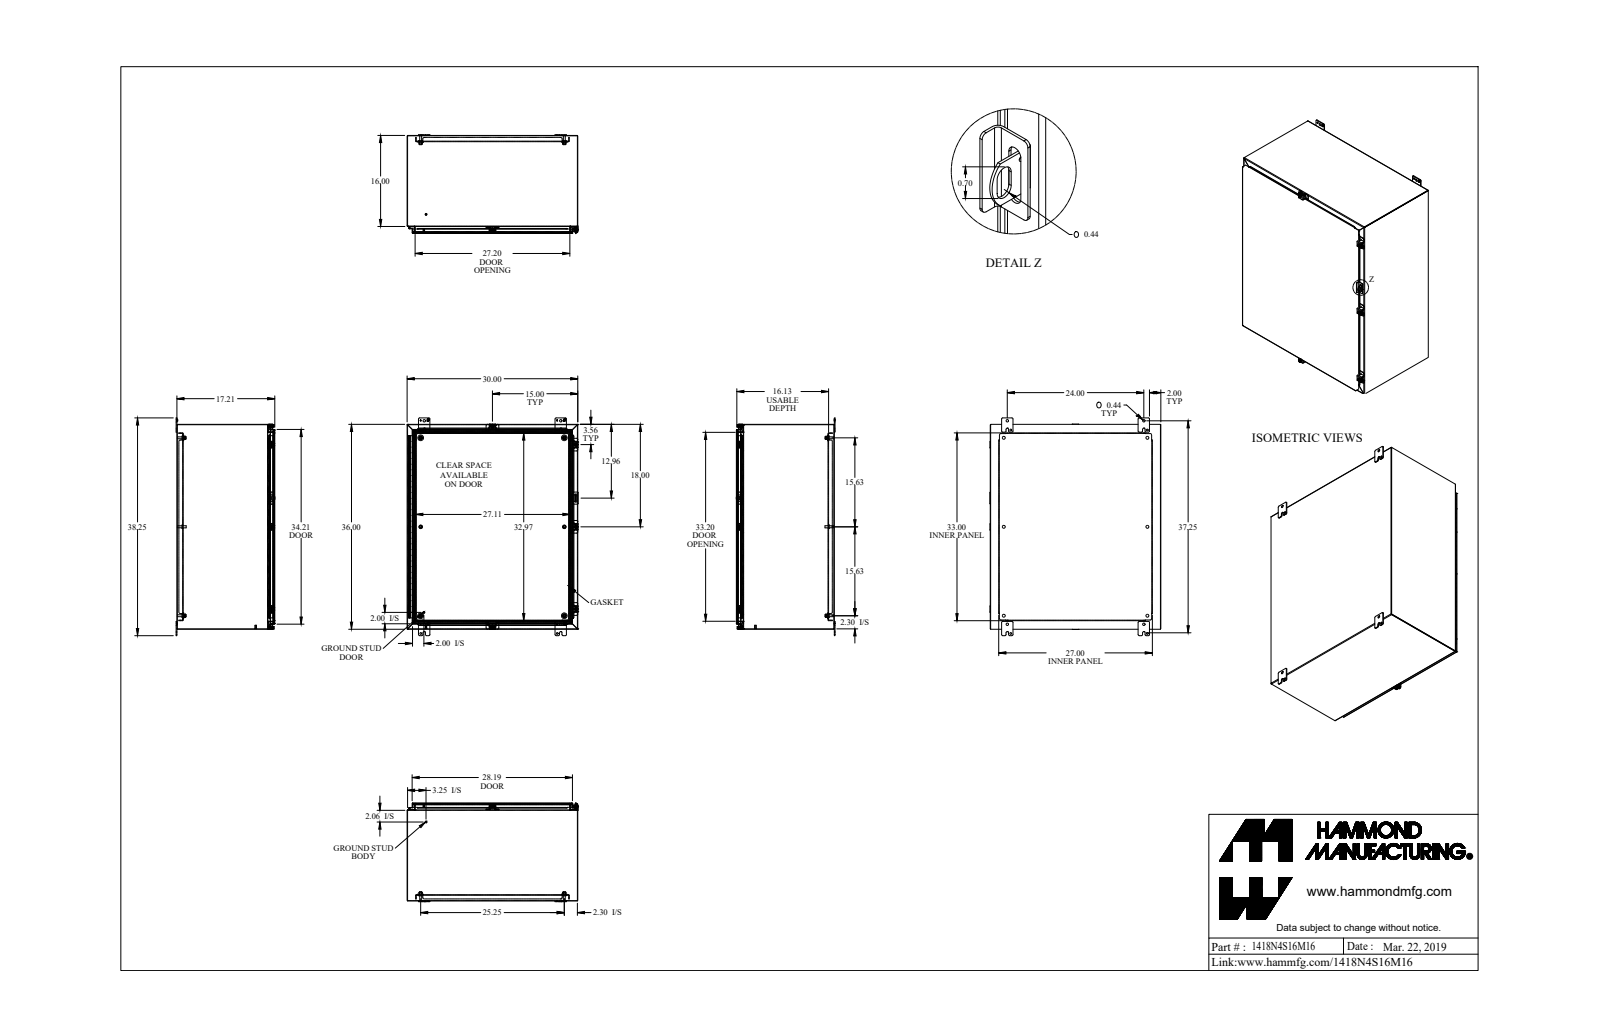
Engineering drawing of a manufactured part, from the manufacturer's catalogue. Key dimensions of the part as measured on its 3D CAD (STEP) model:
Part name (STEP PRODUCT): 1418N4S16M16_Default
STEP written by: SolidWorks 2019 (CONFIG_CONTROL_DESIGN)
Units: inches
Bodies: 51 solids, 1660 faces (880 planar, 636 cylindrical, 144 other)
Overall size (bounding box): 38.25 × 30.063 × 17.375
Volume: 440.5 in³ · Surface area: 11 623 in²
Round holes (diameter × count): ⌀0.5 ×6, ⌀0.213 ×5, ⌀0.265 ×5, ⌀0.375 ×5, ⌀0.307 ×4, ⌀0.313 ×4, ⌀0.437 ×4, ⌀0.445 ×4, ⌀0.11 ×1, ⌀0.125 ×1
Round bosses / shafts (diameter × count): ⌀0.65 ×6, ⌀0.375 ×6, ⌀0.332 ×6, ⌀0.5 ×5, ⌀0.39 ×5, ⌀0.244 ×5, ⌀1 ×4, ⌀0.313 ×2
Partial cylindrical surfaces — rounded edges, fillets, slot ends (radius × count): R0.25 ×32, R0.048 ×27, R0.143 ×27, R0.188 ×26, R0.036 ×22, R0.108 ×22, R0.125 ×14, R0.141 ×10
Main face-to-face distances: 0.072, 29.928, 17.066, 17.138, 0.072, 17.138, 0.095, 17.21, 35.928, 0.937
Hole centre spacings: 15.625, 21.782, 24, 43.059, 12.803, 25.25, 34.256, 35.683
